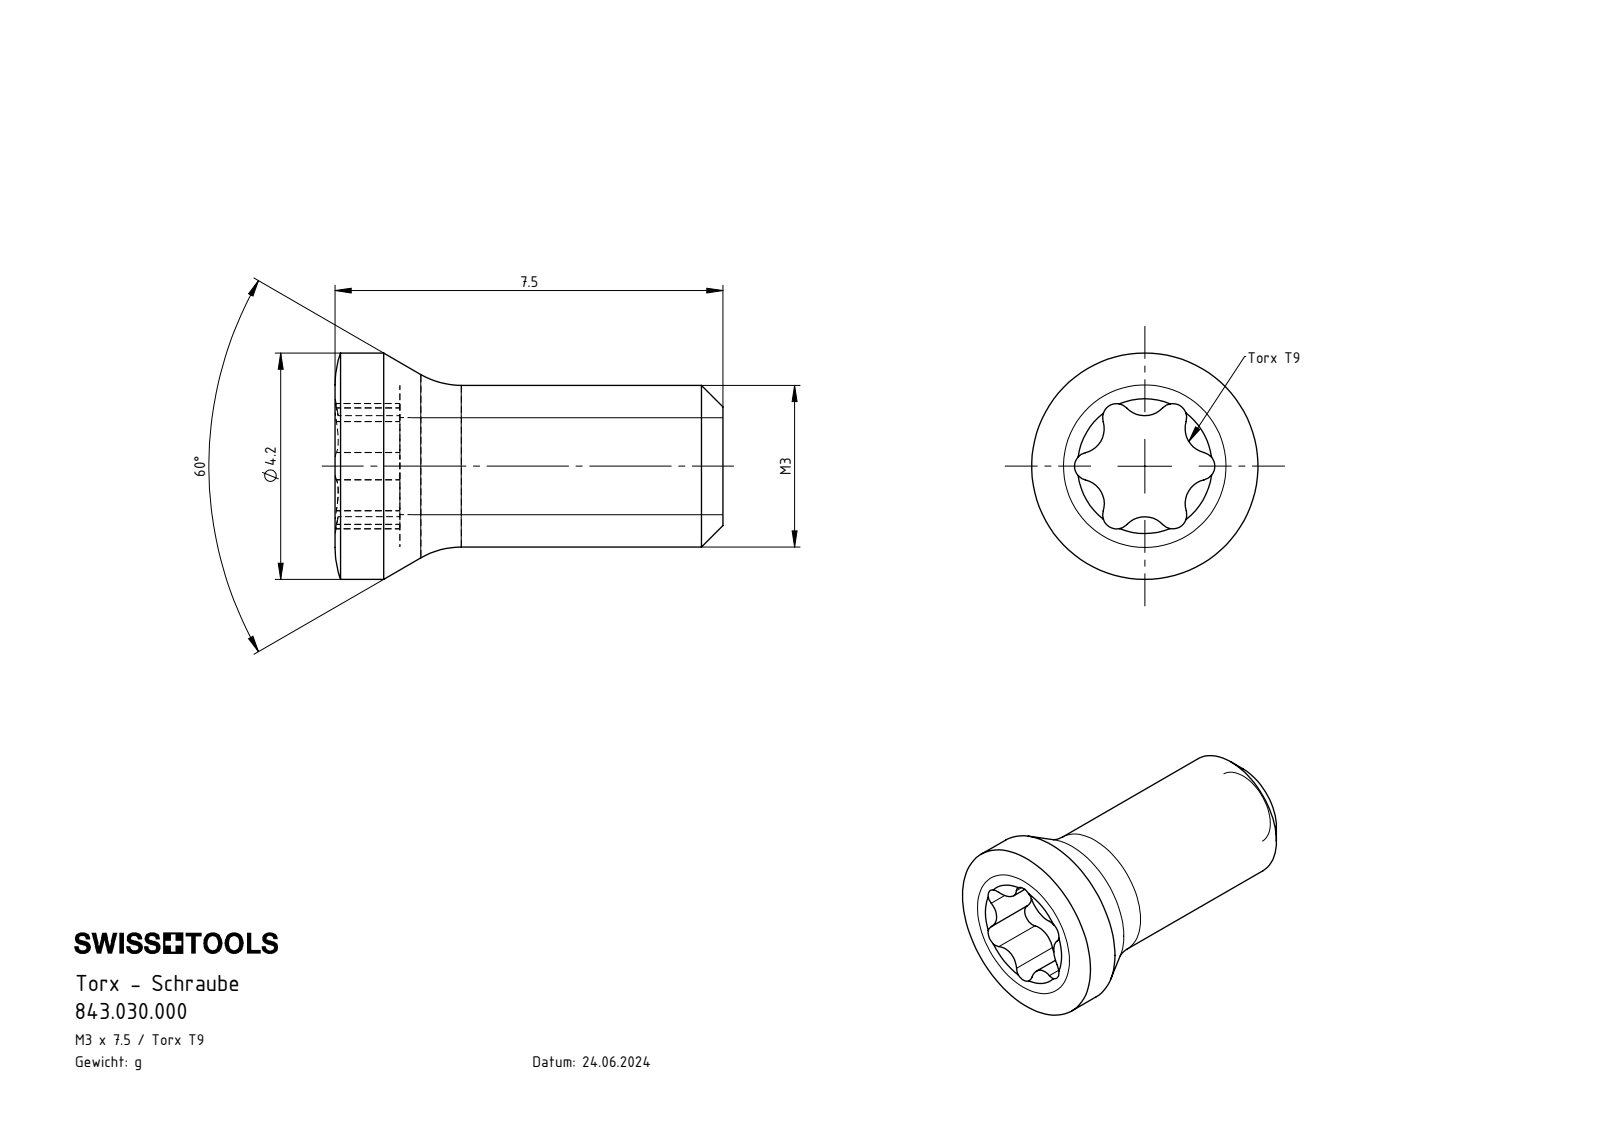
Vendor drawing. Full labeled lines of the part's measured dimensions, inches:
Part name (STEP PRODUCT): 843.030.000
STEP written by: SolidWorks 2022 (AUTOMOTIVE_DESIGN)
Units: inches
Bodies: 1 solid, 37 faces (3 planar, 19 cylindrical, 15 other)
Overall size (bounding box): 0.283 × 0.165 × 0.165
Volume: 0.003 in³ · Surface area: 0.158 in²
Round bosses / shafts (diameter × count): ⌀0.165 ×1, ⌀0.118 ×1
Partial cylindrical surfaces — rounded edges, fillets, slot ends (radius × count): R0.01 ×6, R0.018 ×6
Main face-to-face distances: 0.236, 0.047, 0.283
